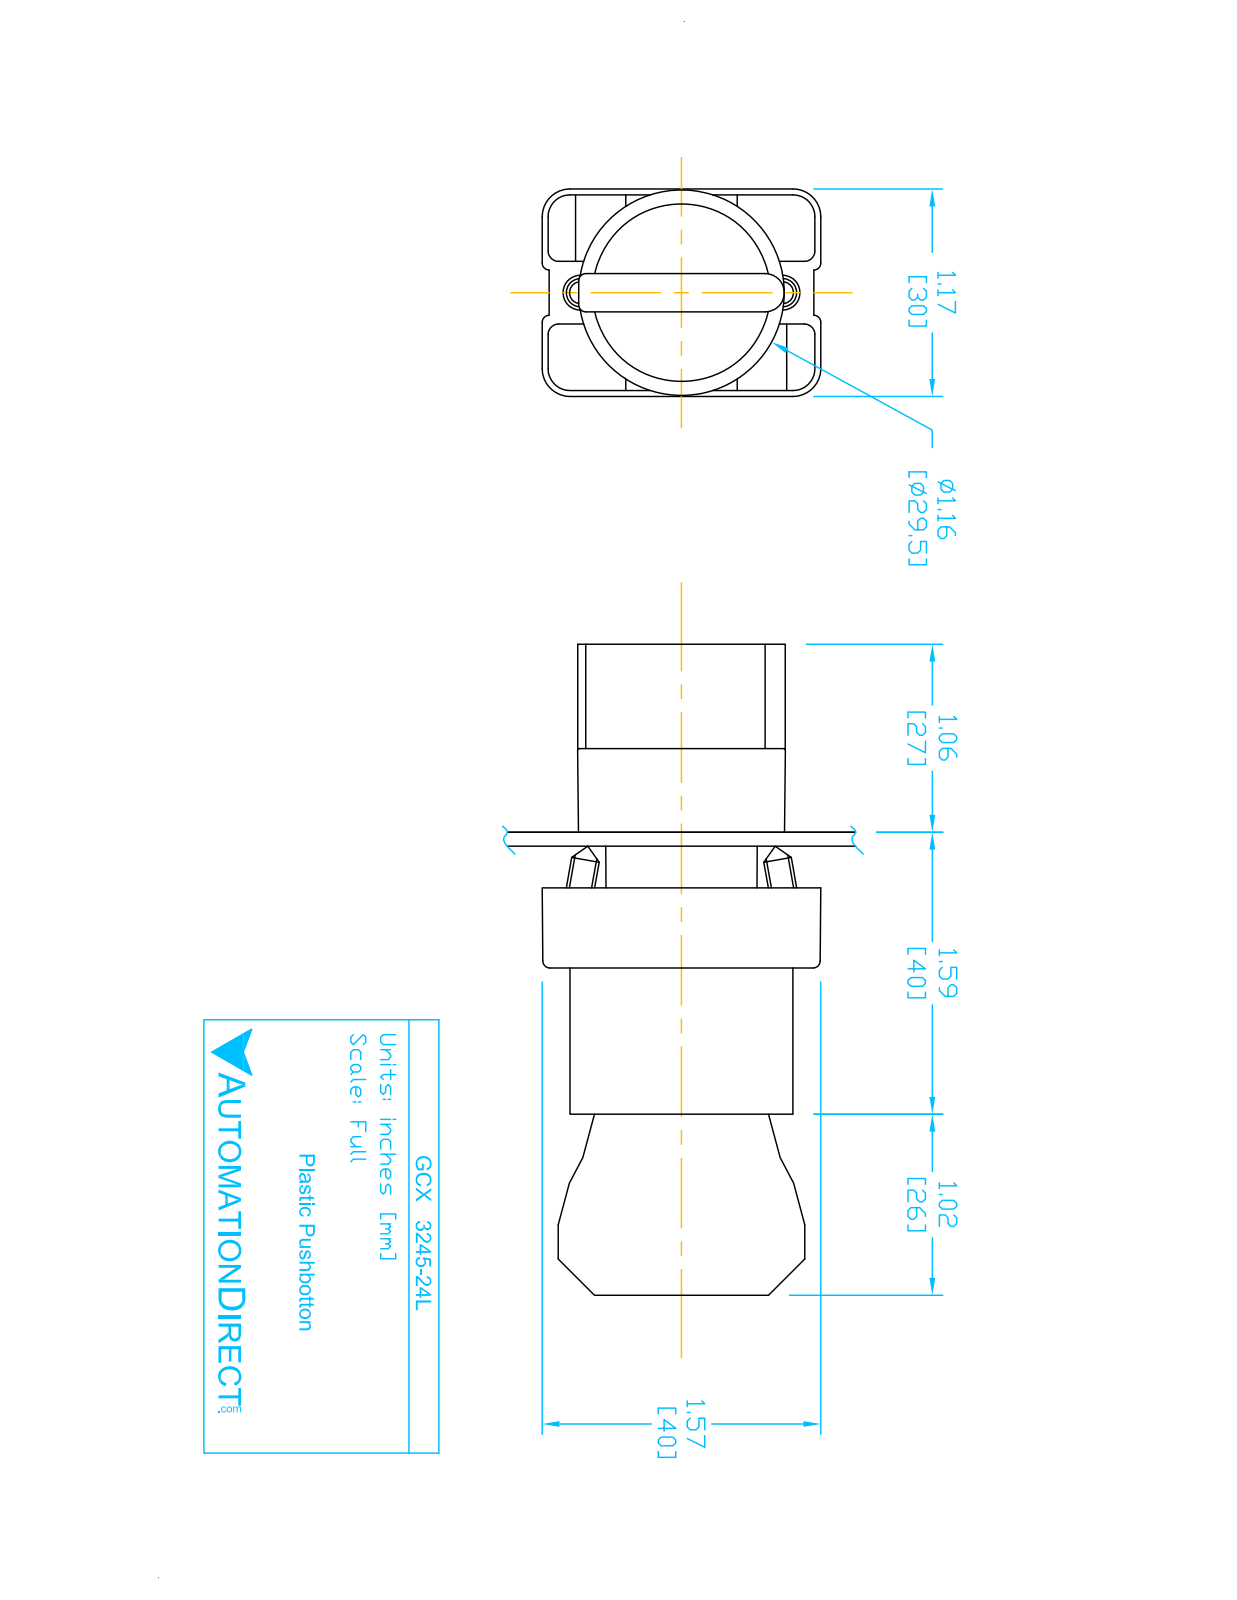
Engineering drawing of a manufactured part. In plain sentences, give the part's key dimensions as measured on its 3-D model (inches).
The part is named "GCX3245L OPERATOR; ECX1050; GCX3245-24L; ECX3029-2 (+1 more)". Its 3-D file was written by "SolidWorks 2016 (AUTOMOTIVE_DESIGN)". It is 8 solids with 445 faces: 263 planar, 151 cylindrical and 31 other. Overall it measures 3.653 by 1.581 by 1.177 inches. Its volume is 2.799 cubic inches and its surface area 39 square inches. Round holes: 2 of diameter 0.079, 2 of diameter 0.124, 2 of diameter 0.13, 1 of diameter 0.087, 1 of diameter 0.197, 1 of diameter 0.469, 1 of diameter 0.878, 1 of diameter 0.888, 1 of diameter 1.024. Round bosses or shafts: 4 of diameter 0.157, 1 of diameter 1.175, 1 of diameter 1.004, 1 of diameter 0.945, 1 of diameter 0.856, 1 of diameter 0.78, 1 of diameter 0.504. Partial cylindrical surfaces (rounded edges, fillets, slot ends): 24 of radius 0.059, 12 of radius 0.041, 12 of radius 0.124, 12 of radius 0.157, 9 of radius 0.039, 2 of radius 0.128, 1 of radius 0.02, 1 of radius 0.063. The main face-to-face distances are 0.827, 2.02, 1.193, 0.579, 1.244, 1.171, 0.472, 0.469, 0.031, 0.033. The hole center spacings are 0.236, 0.544, 0.472, 0.49.
